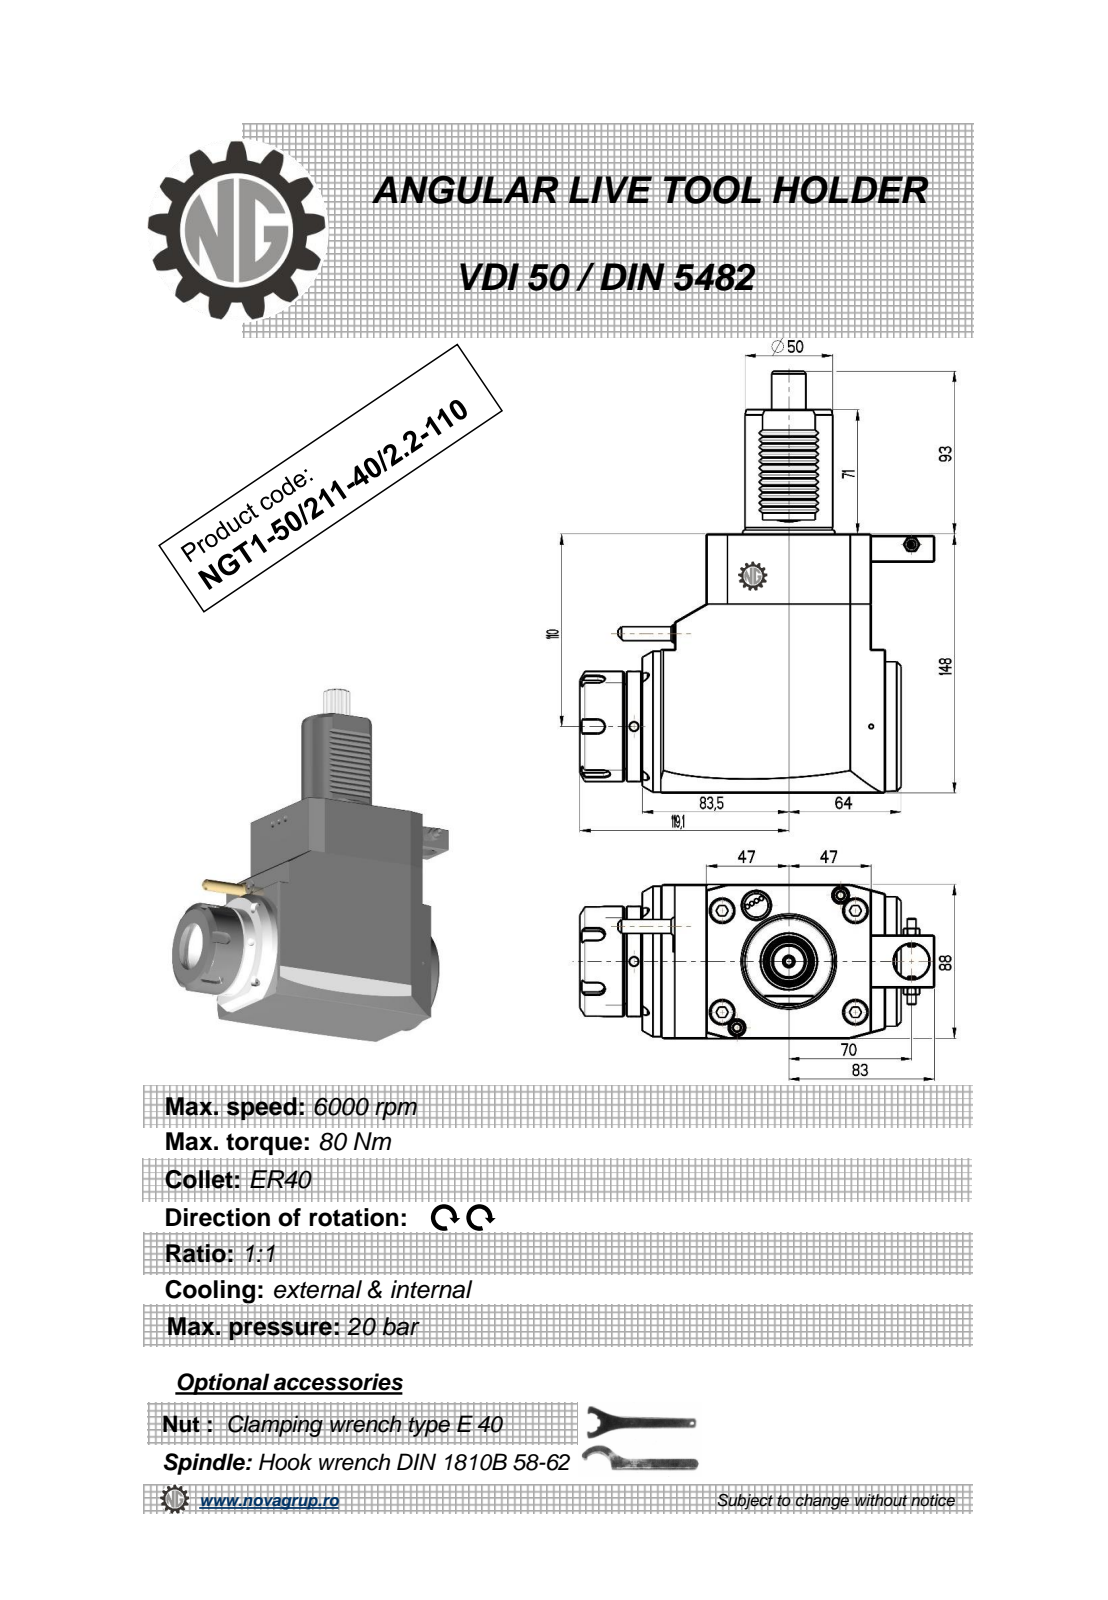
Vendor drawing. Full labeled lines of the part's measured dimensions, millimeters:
Part name (STEP PRODUCT): NGT1_50_211_40_1_2_110
STEP written by: PRO/ENGINEER BY PARAMETRIC TECHNOLOGY CORPORATION, 2010280 (CONFIG_CONTROL_DESIGN)
Units: millimetres
Bodies: 1 solid, 490 faces (203 planar, 145 cylindrical, 142 other)
Overall size (bounding box): 241 × 202.1 × 88
Volume: 1 830 000 mm³ · Surface area: 115 084 mm²
Round holes (diameter × count): ⌀5 ×3, ⌀3 ×1, ⌀4.2 ×1, ⌀4.5 ×1, ⌀5.3 ×1, ⌀9.5 ×1, ⌀20 ×1, ⌀33.5 ×1
Round bosses / shafts (diameter × count): ⌀86 ×1, ⌀74 ×1, ⌀63 ×1, ⌀51 ×1, ⌀50 ×1, ⌀10 ×1, ⌀8.96 ×1, ⌀8 ×1
Partial cylindrical surfaces — rounded edges, fillets, slot ends (radius × count): R3.33 ×24, R0.26 ×12, R0.3 ×12, R0.2 ×6, R3.75 ×5, R2.5 ×1, R8.25 ×1, R9.75 ×1
Main face-to-face distances: 88, 148, 147.5, 17, 8, 94, 111, 9, 36.5, 130.5
Hole centre spacings: 52.46, 56.65, 70, 88.25, 101.5, 158.25
